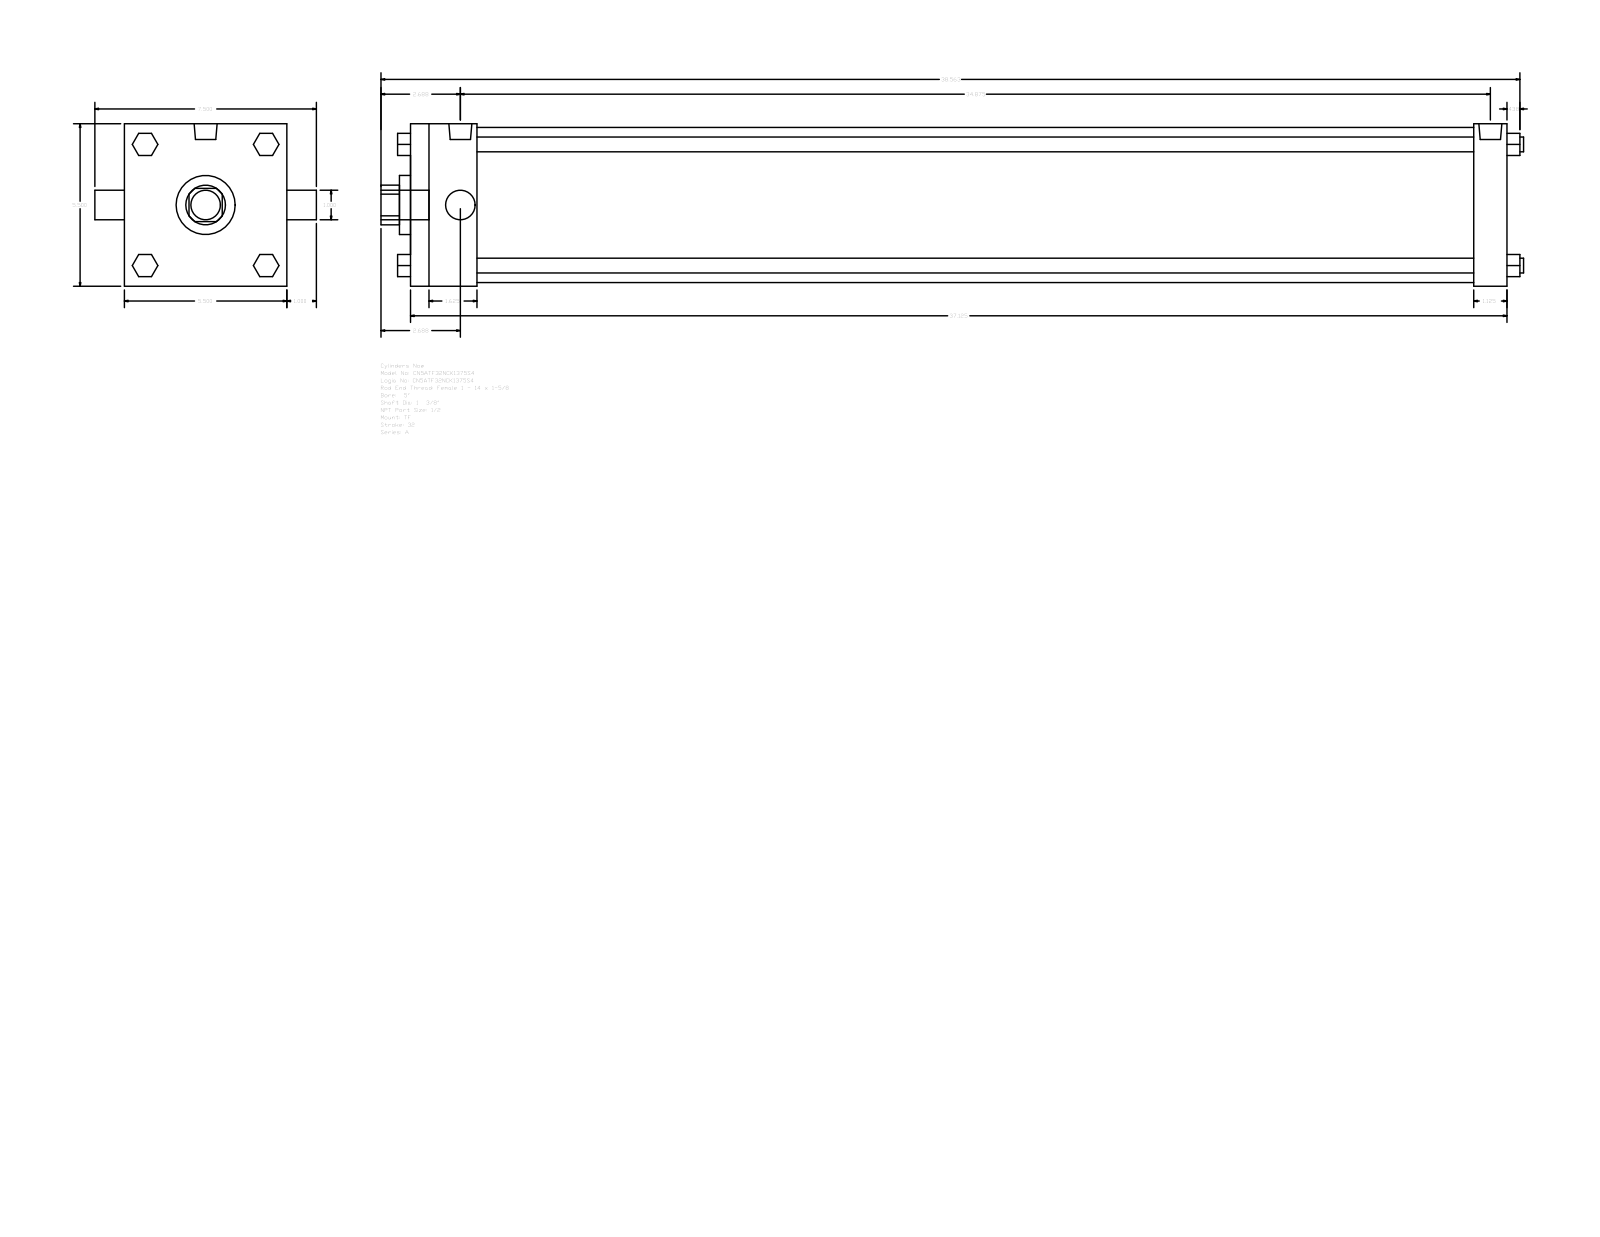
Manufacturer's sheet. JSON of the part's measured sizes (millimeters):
{"part_name": "A_TF__0500_1.375", "step_written_by": "GSSL Pune (CONFIG_CONTROL_DESIGN)", "units": "millimeters", "bodies": {"solids": 0, "faces": 120, "planar": 92, "cylindrical": 28, "other": 0}, "overall_size": [982.66, 190.5, 139.7], "round_holes": [[25.4, 1], [34.92, 1], [50.8, 1], [133.35, 1]], "round_bosses_or_shafts": [[12.7, 4], [8.73, 3], [19.77, 2], [25.4, 1]], "partial_cylinders_radius": [[17.06, 1]], "face_to_face_distances": [139.7, 942.98, 28.58, 914.4, 57.15, 857.25, 885.83, 19.05, 52.07, 90.18]}
